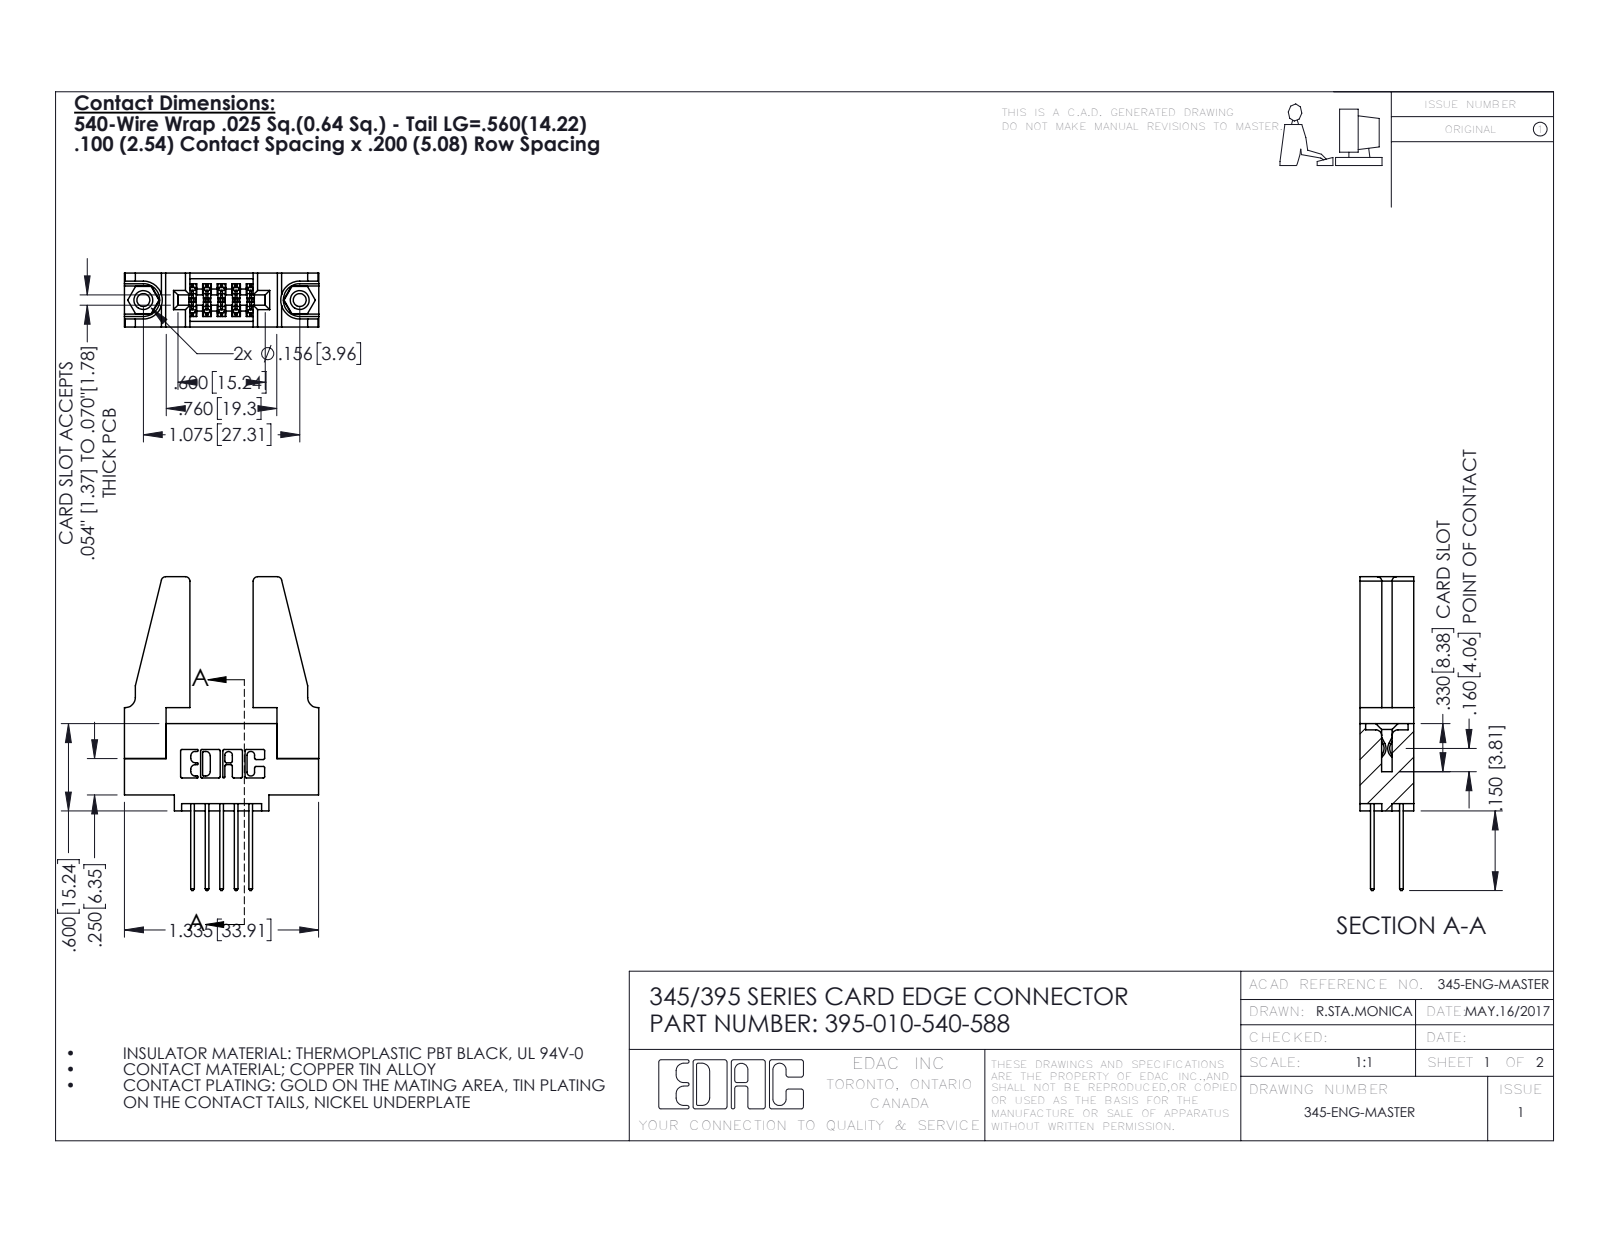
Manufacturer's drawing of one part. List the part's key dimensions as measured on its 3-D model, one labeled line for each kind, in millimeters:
Part name (STEP PRODUCT): 345-220-078_345-220-088; 345 Part_0.110 Offset - 0.156 Dia-TH; 345-250-001_345-250-001-102; 345-292-001_345-293-140 (+1 more)
STEP written by: SolidWorks 2016 (CONFIG_CONTROL_DESIGN)
Units: millimetres
Bodies: 15 solids, 754 faces (486 planar, 252 cylindrical, 16 other)
Overall size (bounding box): 54.8 × 33.9 × 9.4
Volume: 6 180 mm³ · Surface area: 6 987 mm²
Round holes (diameter × count): ⌀2.3 ×2, ⌀3.2 ×2, ⌀4 ×2, ⌀1.6 ×1
Round bosses / shafts (diameter × count): ⌀3.9 ×2
Partial cylindrical surfaces — rounded edges, fillets, slot ends (radius × count): R0.3 ×22, R0.2 ×15, R0.3 ×10, R0.8 ×8, R0.2 ×6, R0.8 ×6, R0.7 ×3, R0.4 ×2
Main face-to-face distances: 9.4, 1.8, 7.6, 5.1, 2.5, 6.9, 0.6, 5.7, 3.8, 3.8
Hole centre spacings: 6.9, 21.5, 27.3
